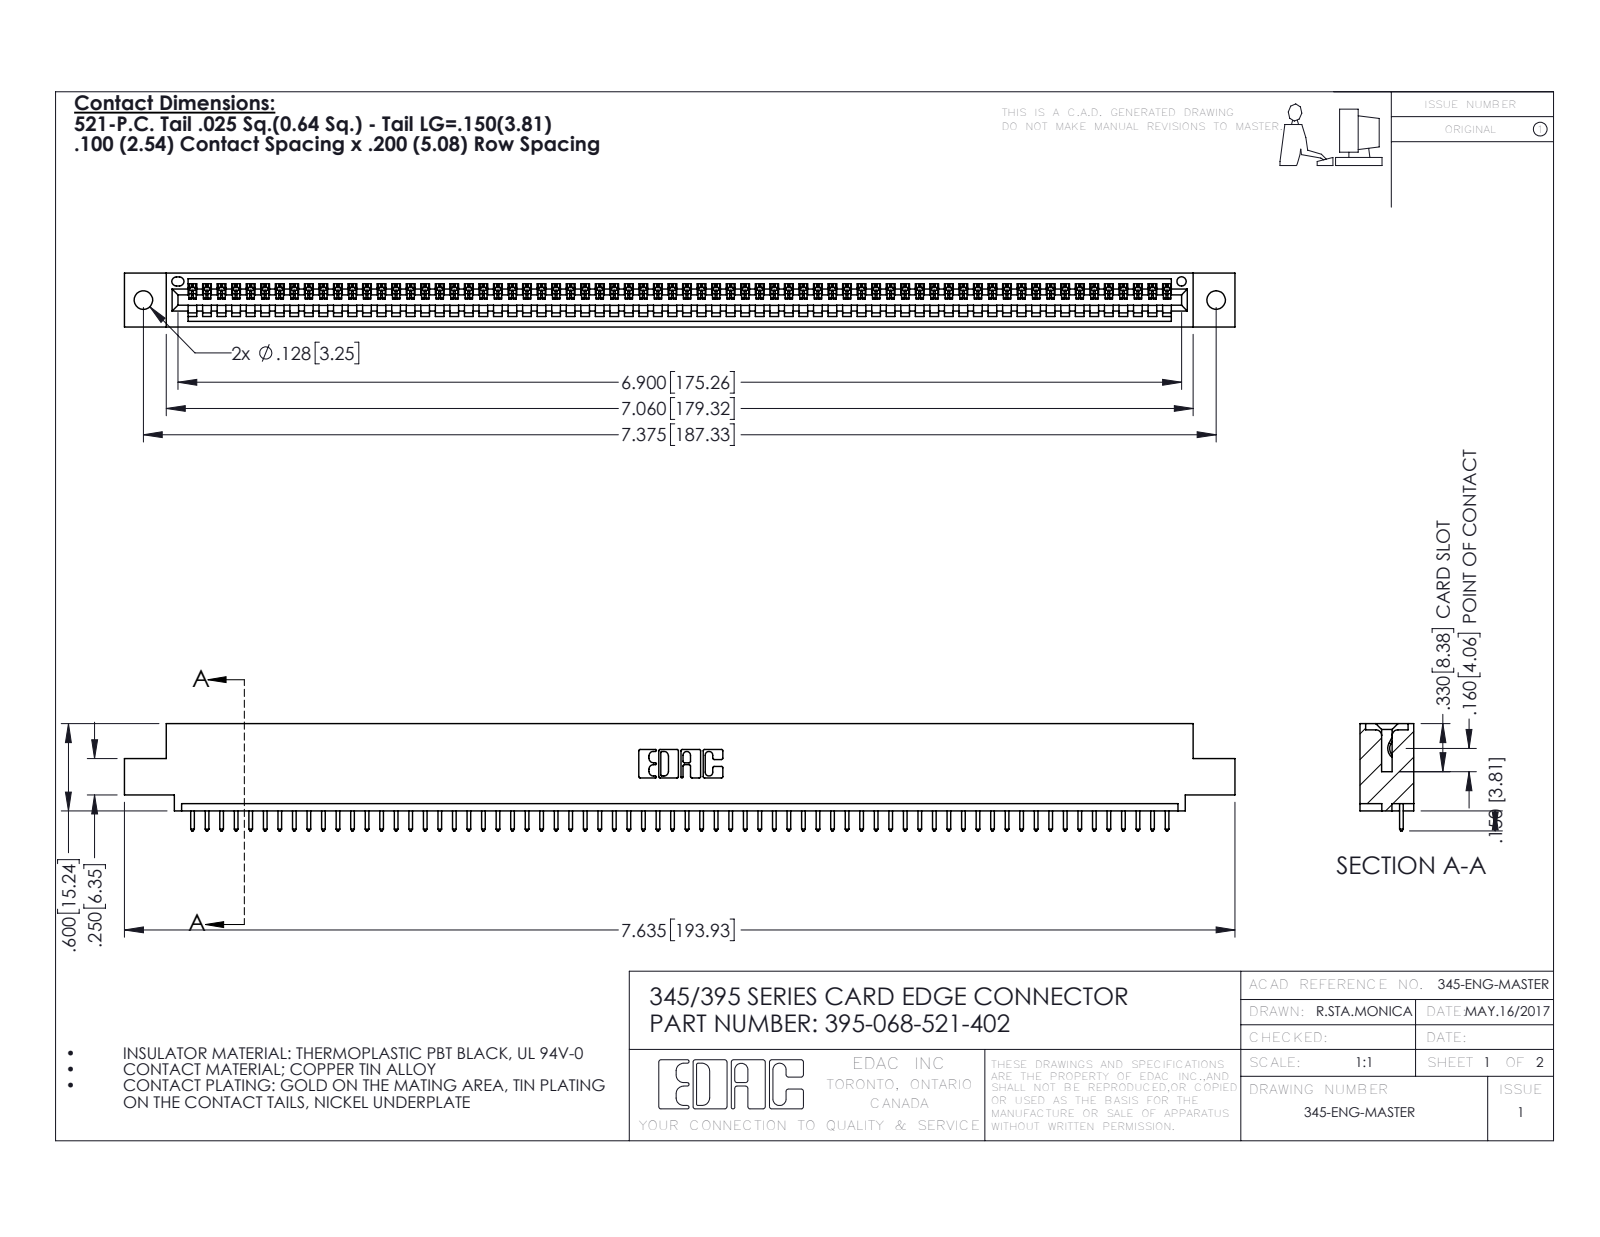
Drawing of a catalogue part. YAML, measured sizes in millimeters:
part_name: "395-068-521-402; 345 Part_0.110 Offset - 0.128 Dia; 345-292-001_345-293-121"
step_written_by: "SolidWorks 2016 (CONFIG_CONTROL_DESIGN)"
units: millimeters
bodies: {solids: 69, faces: 4074, planar: 2804, cylindrical: 1270, other: 0}
overall_size: [193.9, 18.7, 9.4]
volume: 18340
surface_area: 23770
round_holes:
  - {diameter: 3.3, count: 2}
  - {diameter: 1.6, count: 1}
partial_cylinders:
  - {radius: 0.2, count: 136}
  - {radius: 0.3, count: 136}
  - {radius: 0.3, count: 22}
  - {radius: 0.2, count: 6}
  - {radius: 0.8, count: 6}
  - {radius: 0.7, count: 3}
  - {radius: 0.8, count: 2}
  - {radius: 1, count: 2}
face_to_face_distances: [7.6, 1.8, 9.4, 5.1, 2.5, 6.9, 0.6, 5.7, 3.8, 1.8]
hole_center_spacings: [6.9, 181.3, 187.3]
